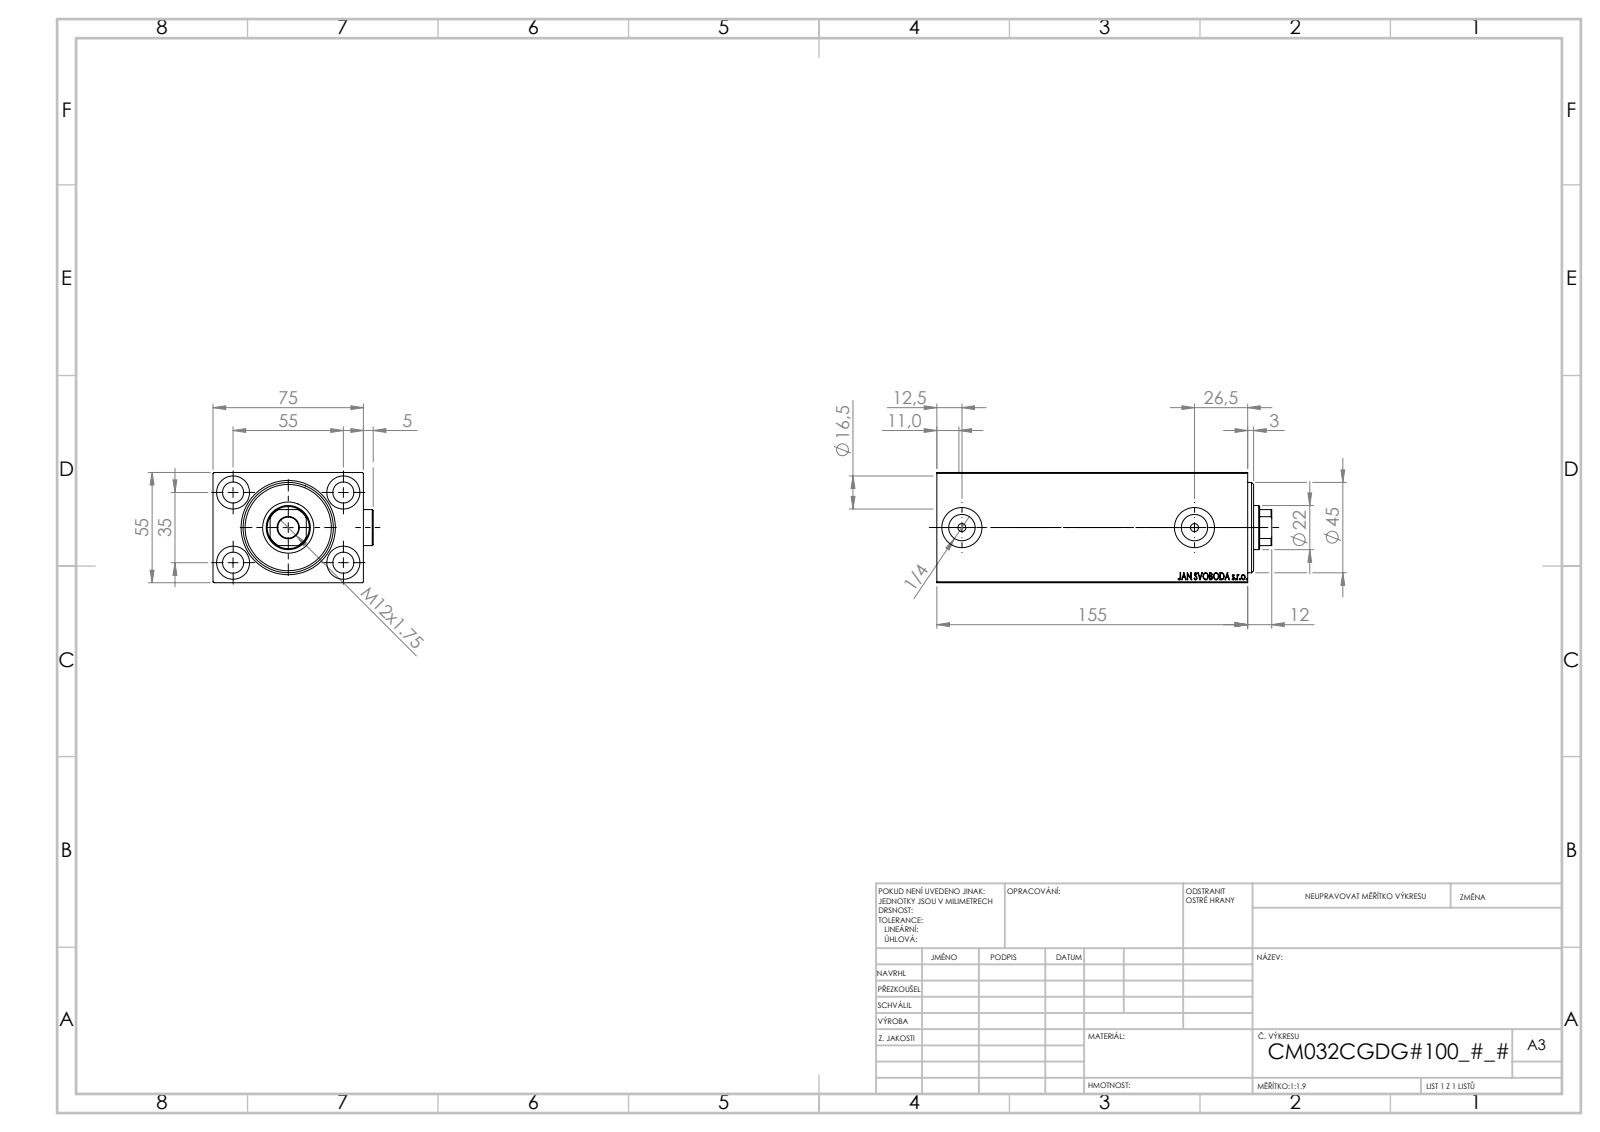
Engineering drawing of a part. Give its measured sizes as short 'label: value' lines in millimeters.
name: Zatka_OIL_PORT; V450CM_C_VCP; V450CM_VC_B; V450CM_C_Body
written by: SolidWorks 2019 (CONFIG_CONTROL_DESIGN)
unit: mm
bodies: 5 solids, 916 faces (442 planar, 76 cylindrical, 398 other)
size: 167 × 79.9 × 55
volume: 532 497 mm³; area: 108 124 mm²
holes: 5× ⌀10.5, 4× ⌀16.5, 2× ⌀4, 2× ⌀13.16, 2× ⌀20, 1× ⌀22, 1× ⌀25.5, 1× ⌀32, 1× ⌀34, 1× ⌀45
bosses: 2× ⌀18
rounds: 1× R10.5
face distances: 55, 75, 5, 10, 145, 155, 150, 140, 74.9, 133
hole spacings: 32.6, 35, 55, 65.19, 116
